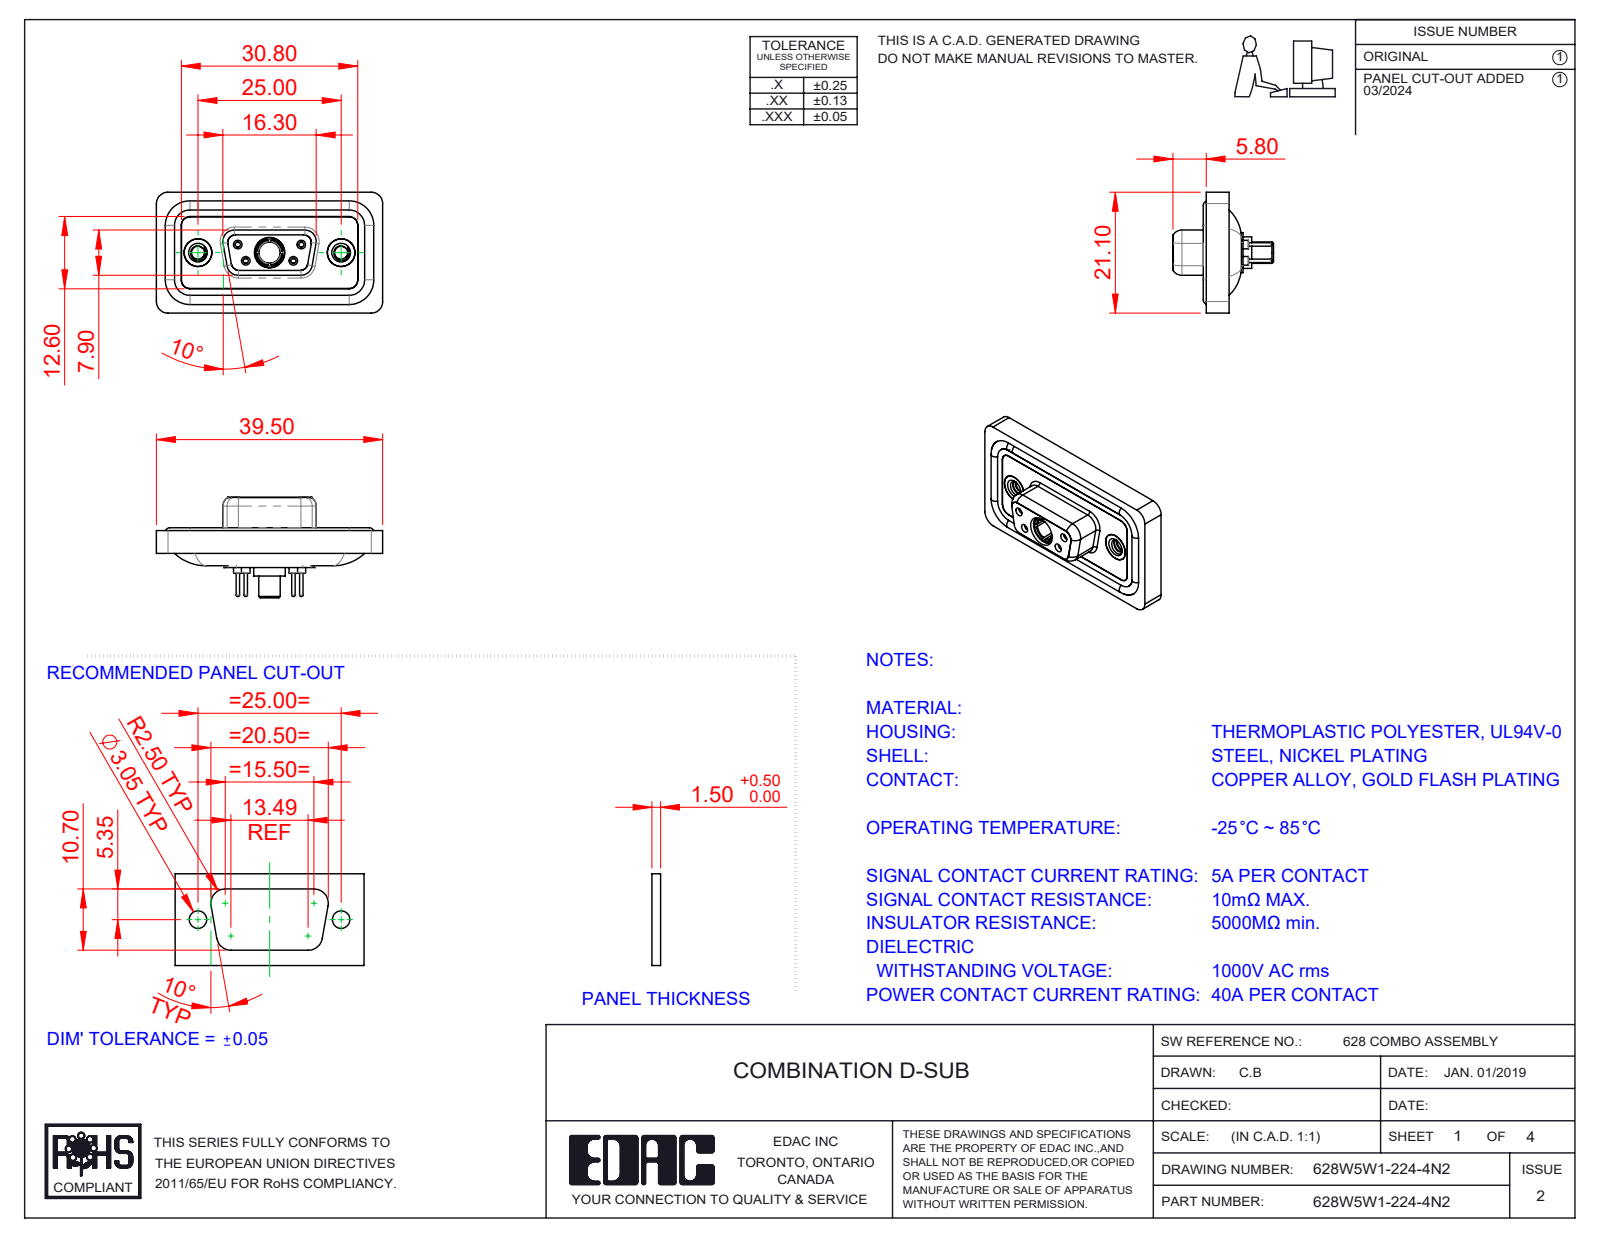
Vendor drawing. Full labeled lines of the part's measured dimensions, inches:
Part name (STEP PRODUCT): 628Combo Contact Row 2_24; 628W5W1-224-4N2; Power Socket_40A S; 628Combo Threaded Rivet_2 (+5 more)
STEP written by: SolidWorks 2023 (CONFIG_CONTROL_DESIGN)
Units: inches
Bodies: 13 solids, 680 faces (194 planar, 287 cylindrical, 199 other)
Overall size (bounding box): 1.555 × 0.831 × 0.691
Volume: 0.292 in³ · Surface area: 11.85 in²
Round holes (diameter × count): ⌀0.035 ×4, ⌀0.043 ×4, ⌀0.059 ×4, ⌀0.079 ×4, ⌀0.191 ×3, ⌀0.063 ×2, ⌀0.067 ×2, ⌀0.089 ×2, ⌀0.157 ×2, ⌀0.159 ×2, ⌀0.197 ×2, ⌀0.146 ×1
Round bosses / shafts (diameter × count): ⌀0.063 ×6, ⌀0.087 ×4, ⌀0.024 ×4, ⌀0.195 ×2, ⌀0.189 ×2, ⌀0.217 ×1, ⌀0.205 ×1, ⌀0.195 ×1
Partial cylindrical surfaces — rounded edges, fillets, slot ends (radius × count): R0.059 ×22, R0.079 ×18, R0.053 ×8, R0.063 ×8, R0.01 ×4, R0.02 ×4, R0.024 ×4, R0.026 ×4
Main face-to-face distances: 0.016, 0.114, 0.043, 0.071, 0.063, 0.02, 0.222, 0.293, 0.211, 0.142
Hole centre spacings: 0.124, 0.225, 0.28, 0.492, 0.713, 0.173, 0.173, 0.327
